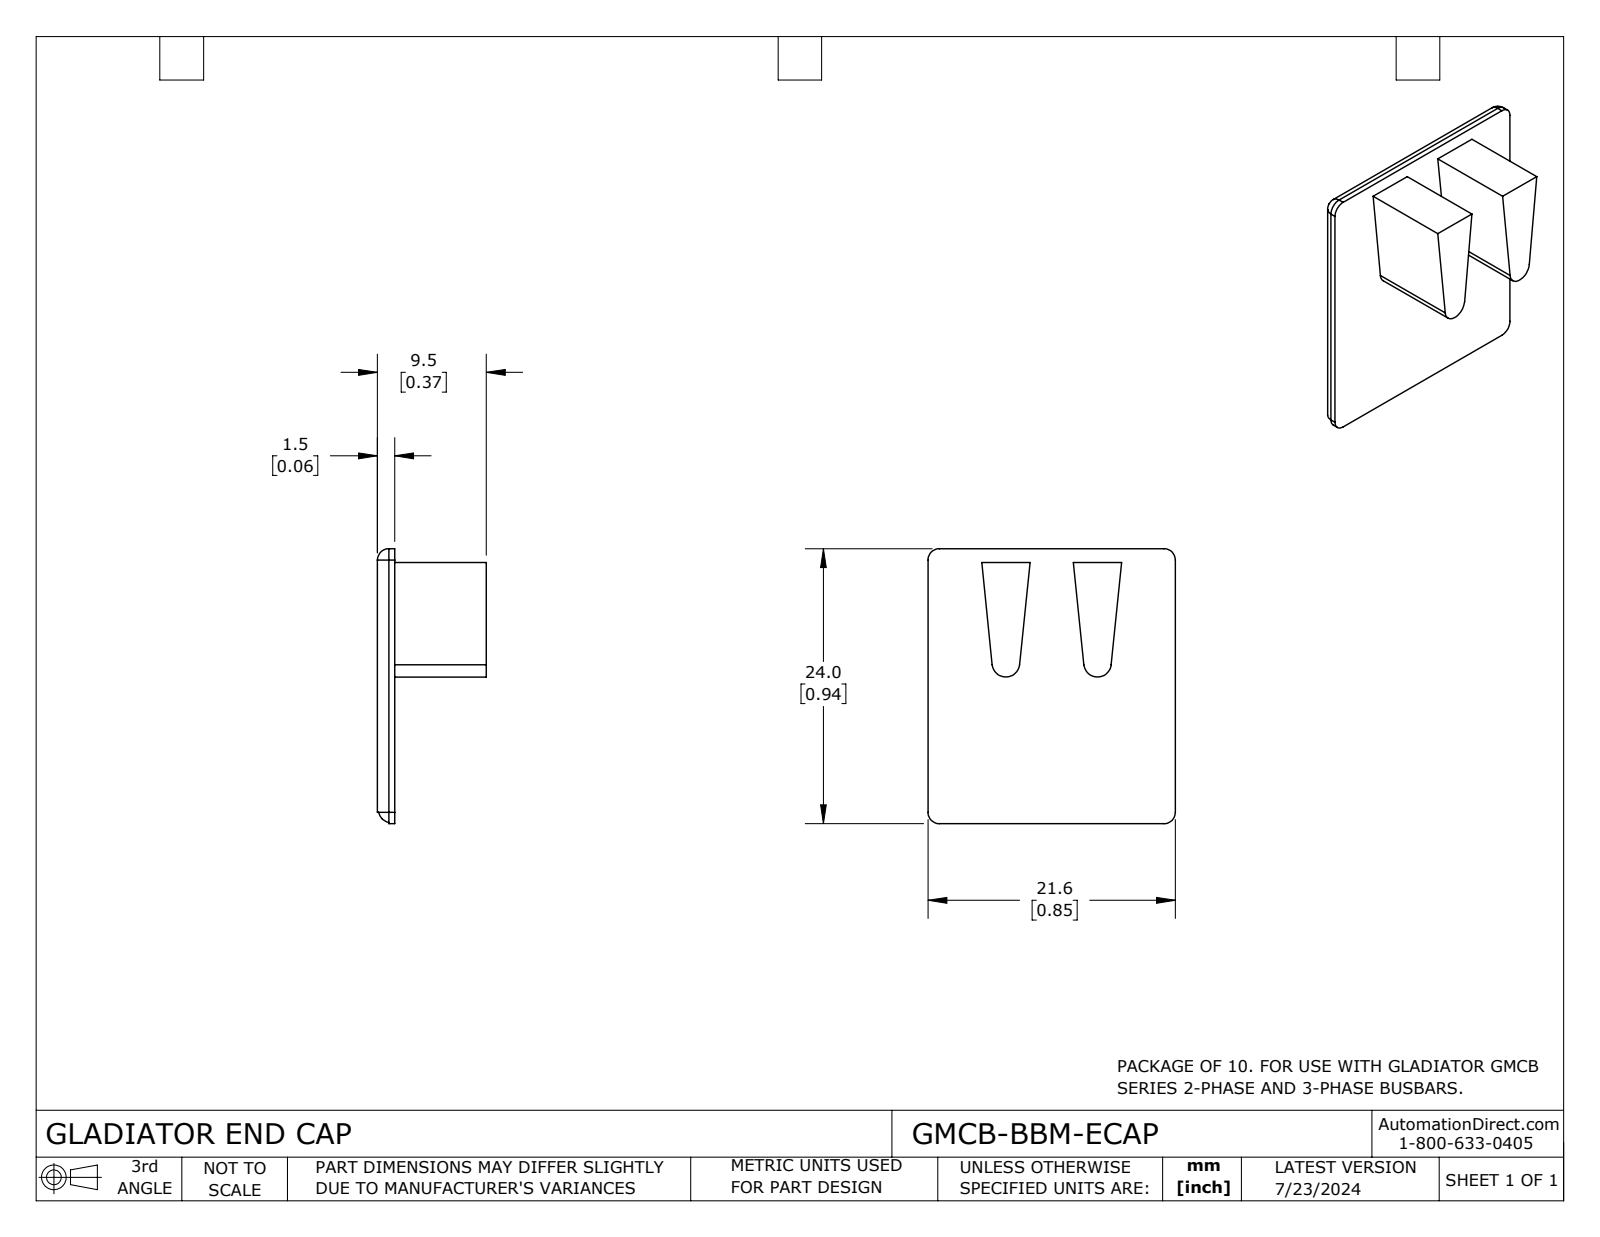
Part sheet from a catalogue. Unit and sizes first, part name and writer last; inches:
Units: inches
Overall size (bounding box): 0.945 × 0.85 × 0.374
Partial cylindrical surfaces — rounded edges, fillets, slot ends (radius × count): R0.039 ×8, R0.047 ×2
Main face-to-face distances: 0.059, 0.313, 0.374, 0.315, 0.85, 0.047, 0.898, 0.945
Volume: 0.077 in³ · Surface area: 2.389 in²
Bodies: 1 solid, 32 faces (14 planar, 10 cylindrical, 8 other)
Part name (STEP PRODUCT): GMCB-BBM-ECAP
STEP written by: SolidWorks 2023 (CONFIG_CONTROL_DESIGN)
